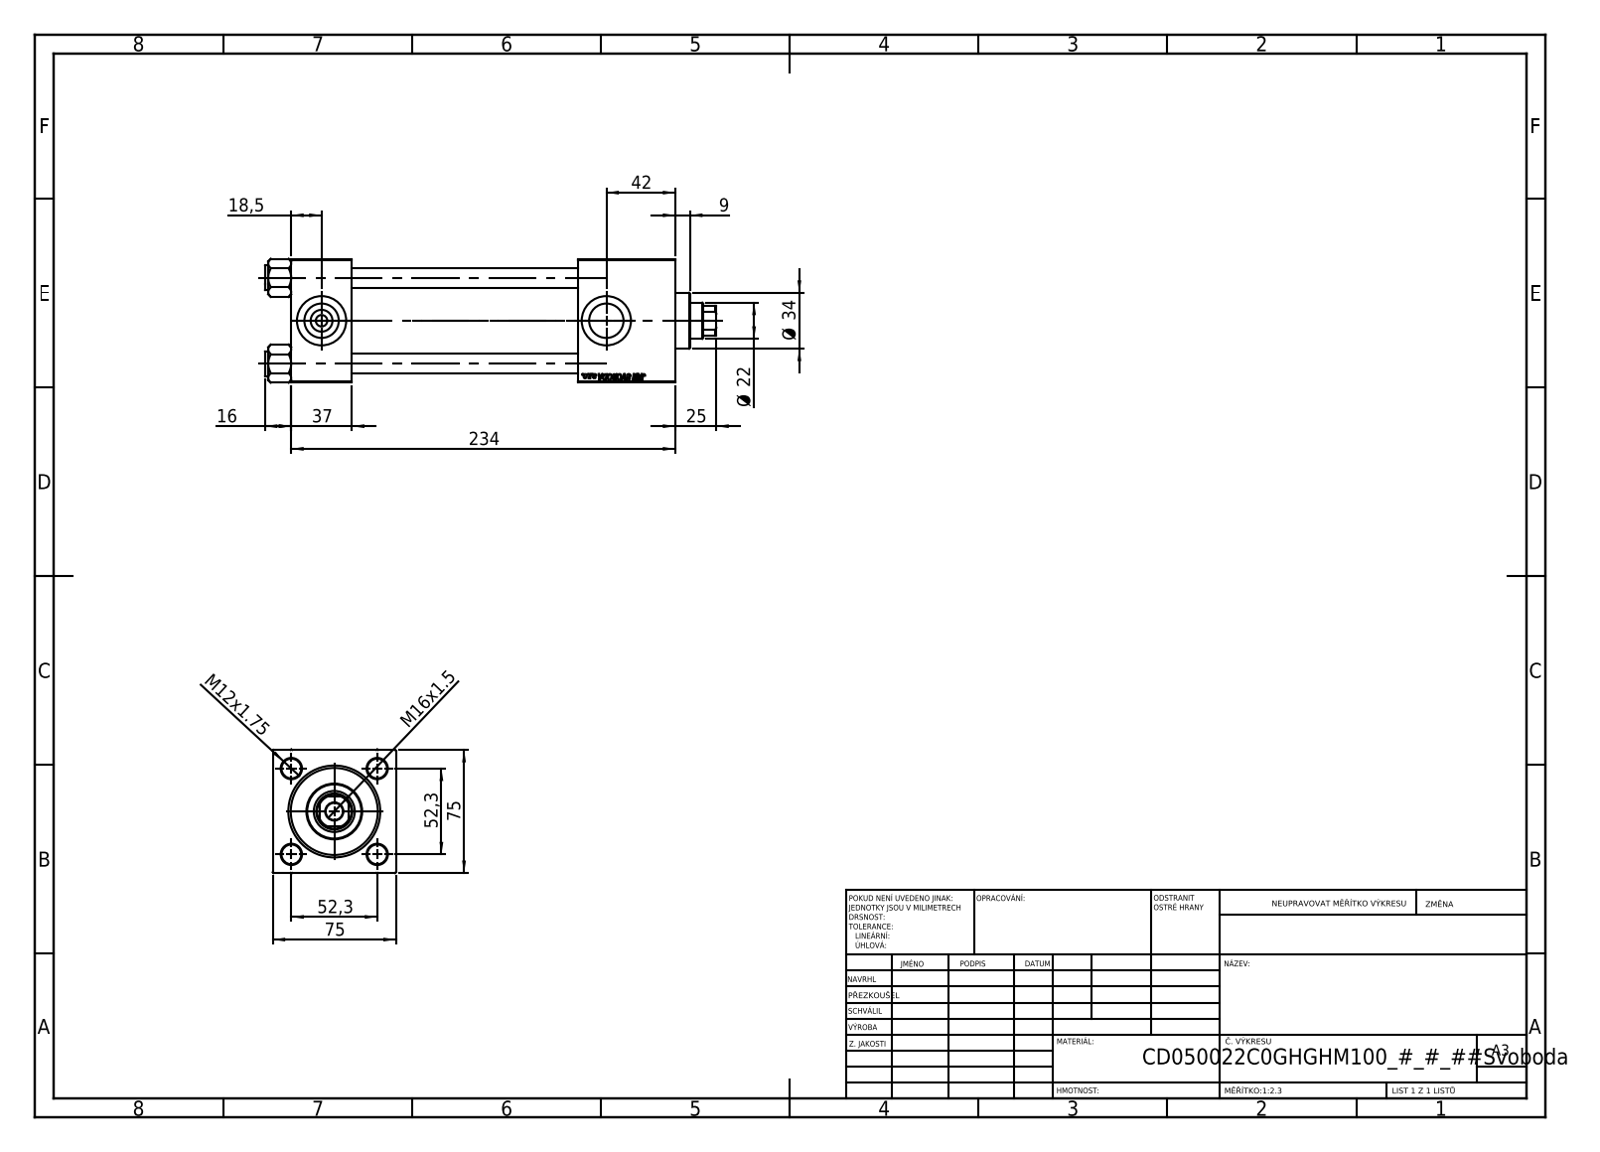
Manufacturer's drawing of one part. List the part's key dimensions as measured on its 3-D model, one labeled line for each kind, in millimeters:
Part name (STEP PRODUCT): V215CD_C_TYCINKA; V215CD_Body_C; V215CD_VC_C; V215CD_VCP_C (+1 more)
STEP written by: SolidWorks 2019 (CONFIG_CONTROL_DESIGN)
Units: millimetres
Bodies: 11 solids, 1148 faces (526 planar, 86 cylindrical, 536 other)
Overall size (bounding box): 275 × 75.54 × 75
Volume: 763 527 mm³ · Surface area: 191 519 mm²
Round holes (diameter × count): ⌀12 ×4, ⌀7 ×2, ⌀20.96 ×2, ⌀30 ×2, ⌀10.5 ×1, ⌀22 ×1, ⌀25 ×1, ⌀41 ×1, ⌀50 ×1, ⌀53 ×1
Round bosses / shafts (diameter × count): ⌀15 ×4, ⌀56 ×1, ⌀34 ×1
Partial cylindrical surfaces — rounded edges, fillets, slot ends (radius × count): R10.5 ×1
Main face-to-face distances: 75, 37, 234, 197, 175, 138, 59, 205.3, 168.3, 30.3
Hole centre spacings: 36.98, 52.3, 73.96, 173.5
